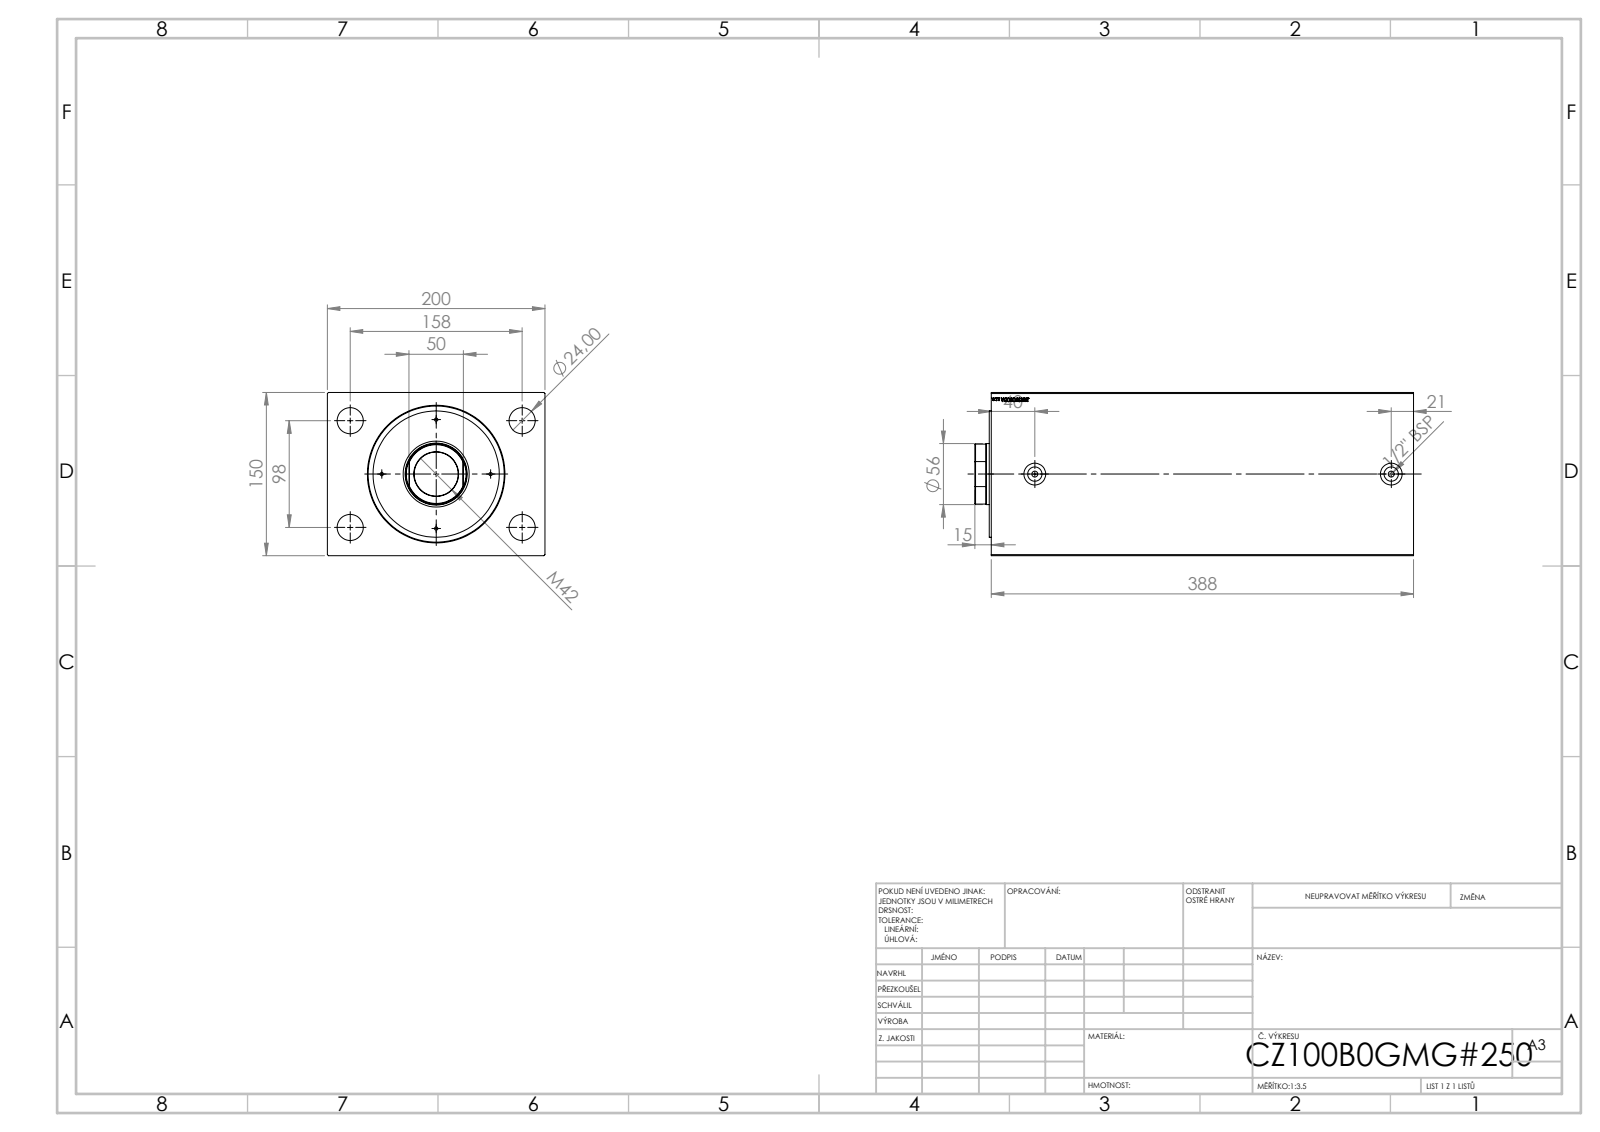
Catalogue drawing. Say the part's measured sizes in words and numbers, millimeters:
The part is named "V500CZ_B_VC; V500CZ". Its 3-D file was written by "SolidWorks 2019 (CONFIG_CONTROL_DESIGN)". It is 3 solids with 874 faces: 400 planar, 58 cylindrical and 416 other. Overall it measures 403 by 200 by 150 millimeters. Its volume is 10 130 000 cubic millimeters and its surface area 589 110 square millimeters. Round holes: 4 of diameter 3, 4 of diameter 24, 2 of diameter 5.5, 2 of diameter 13.16, 2 of diameter 20, 1 of diameter 36, 1 of diameter 40.5, 1 of diameter 56, 1 of diameter 57, 1 of diameter 100, 1 of diameter 125. Round bosses or shafts: 1 of diameter 116. Partial cylindrical surfaces (rounded edges, fillets, slot ends): 1 of radius 27.5. The main face-to-face distances are 150, 200, 388, 354.7, 33.3, 15, 1.8, 13.2, 341.5, 374.8. The hole center spacings are 50, 56.94, 70.71, 79.01, 92.96, 126.66, 137.99, 98.
